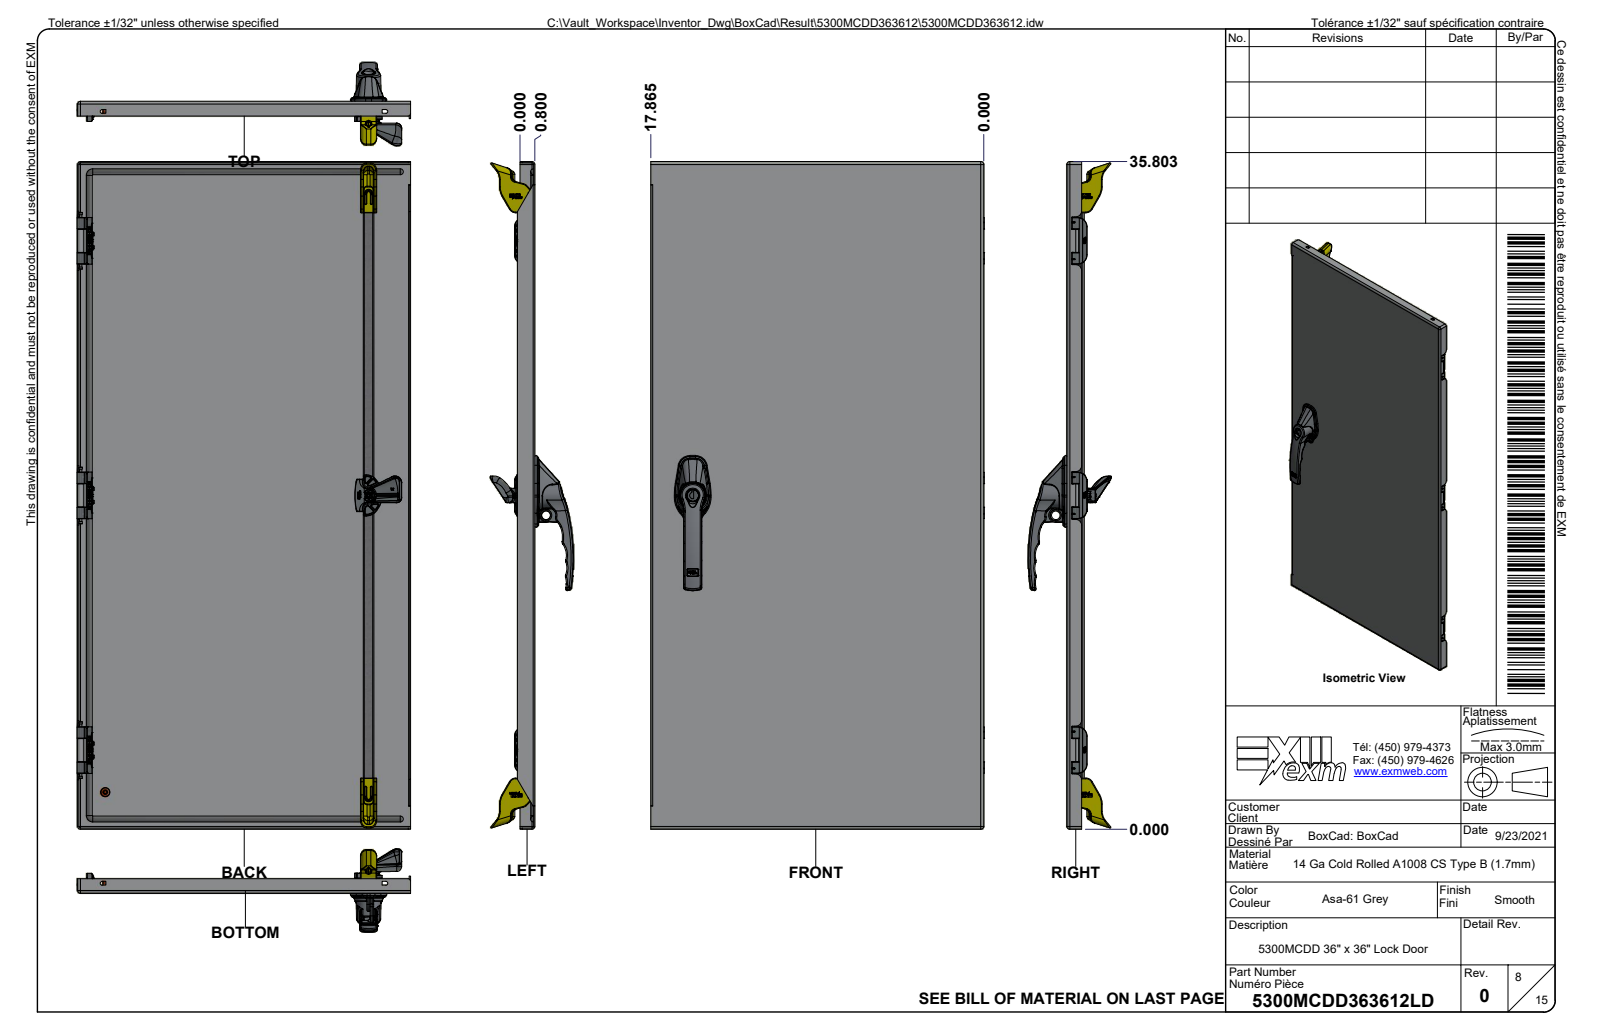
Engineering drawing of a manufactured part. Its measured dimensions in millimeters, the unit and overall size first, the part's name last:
Units: millimetres
Overall size (bounding box): 963.5 × 919.6 × 388.6
Round holes (diameter × count): ⌀7.4 ×22, ⌀1.1 ×18, ⌀0.8 ×14, ⌀4.2 ×10, ⌀8 ×10, ⌀12.7 ×10, ⌀6.9 ×8, ⌀4.5 ×6, ⌀7.7 ×6, ⌀5.1 ×5, ⌀9.9 ×4, ⌀4 ×3
Round bosses / shafts (diameter × count): ⌀1 ×18, ⌀0.8 ×13, ⌀18.2 ×8, ⌀7.9 ×8, ⌀6.7 ×8, ⌀5.9 ×7, ⌀7.6 ×6, ⌀5.1 ×6
Partial cylindrical surfaces — rounded edges, fillets, slot ends (radius × count): R0.5 ×365, R1 ×320, R0.3 ×307, R0.2 ×199, R0.1 ×102, R0.4 ×93, R2 ×83, R0.8 ×62
Main face-to-face distances: 1.7, 331.5, 329.8, 333.2, 1.7, 22.2, 23.9, 307.6, 309.3, 25.7
Hole centre spacings: 923.1, 346.8, 913.1, 952.5, 135.5, 270.9, 381, 406.4
Volume: 7 181 000 mm³ · Surface area: 8 292 000 mm²
Bodies: 126 solids, 20282 faces (6175 planar, 4930 cylindrical, 9177 other)
Part name (STEP PRODUCT): 5300MCDD363612; 5300MCDD363612B; 5300MCDD363612B-P; 5300MCDD363612BT-P (+8 more)
STEP written by: Autodesk Inventor 2024 (AUTOMOTIVE_DESIGN)
